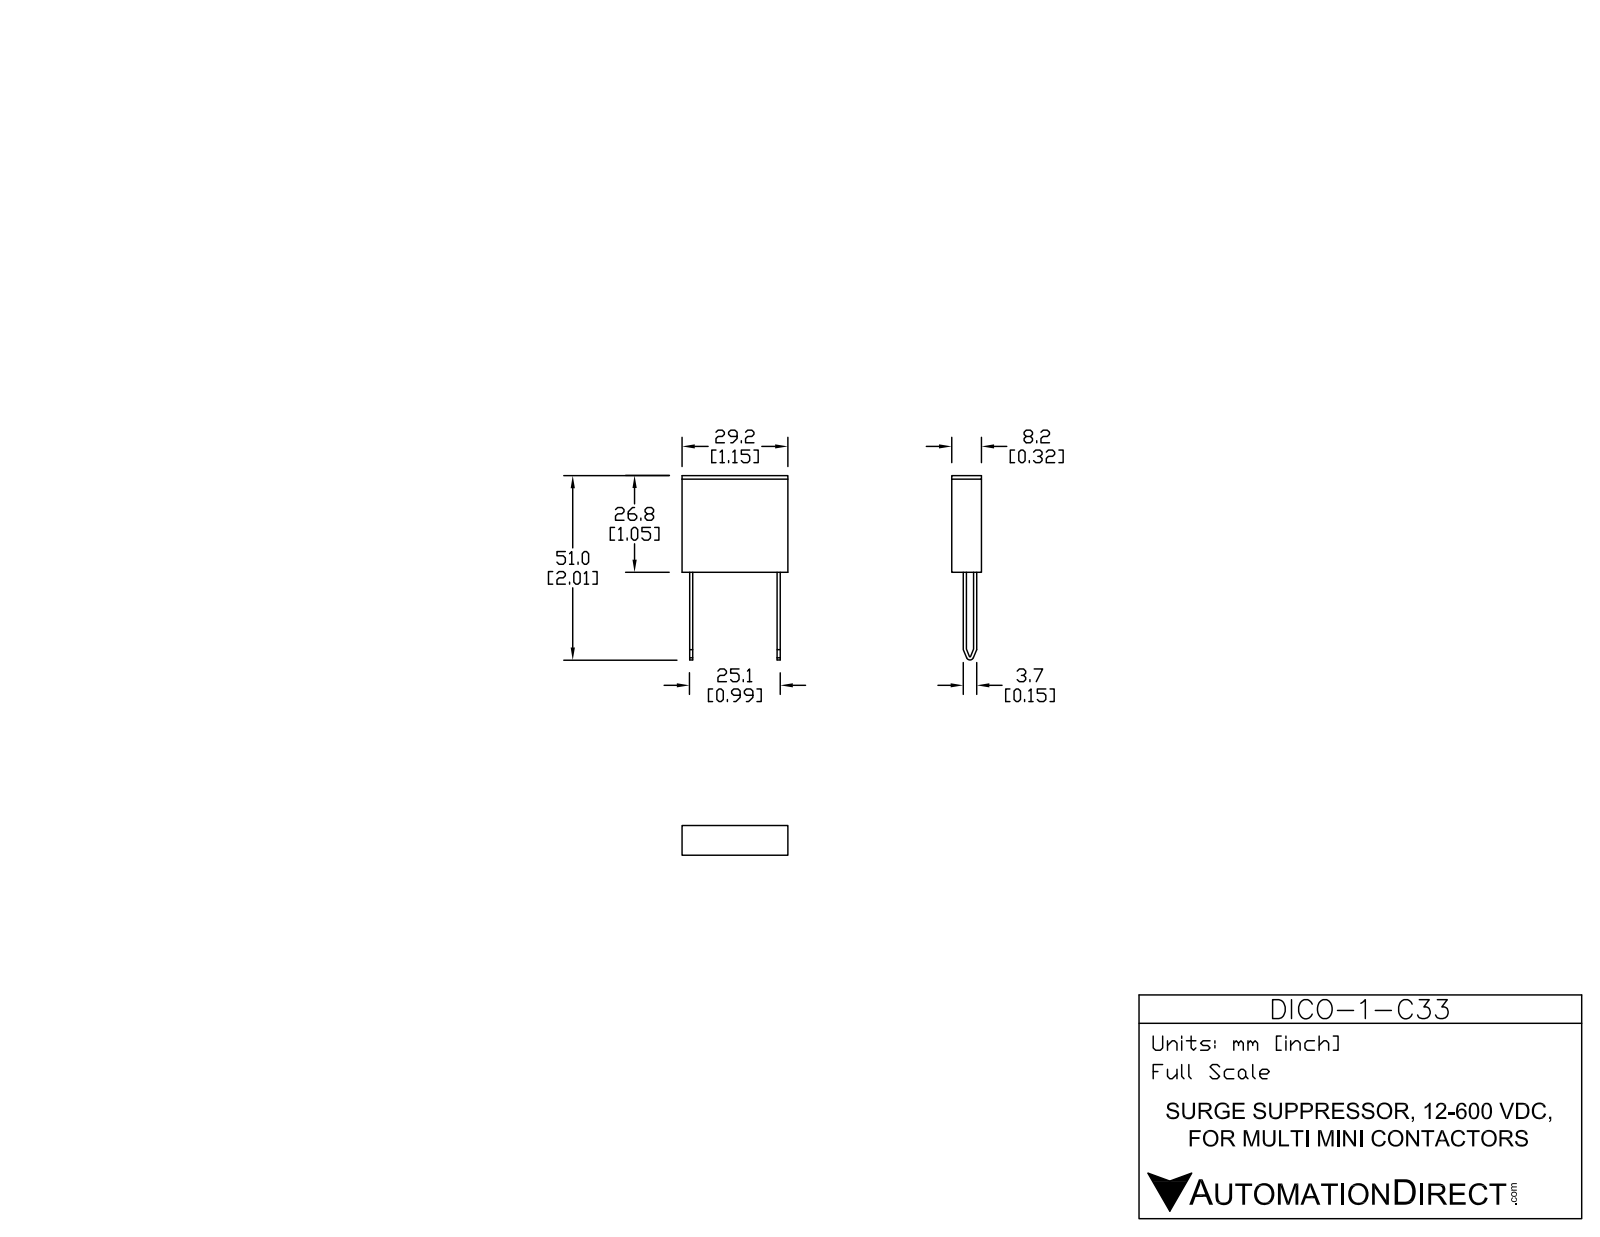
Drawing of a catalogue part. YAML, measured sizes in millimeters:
part_name: "DIC0-1-C33"
step_written_by: "SolidWorks 2013 (AUTOMOTIVE_DESIGN)"
units: millimeters
bodies: {solids: 1, faces: 34, planar: 26, cylindrical: 8, other: 0}
overall_size: [50.9, 29.2, 8.2]
volume: 6463
surface_area: 2803
partial_cylinders:
  - {radius: 0.15, count: 1}
  - {radius: 1, count: 1}
face_to_face_distances: [8.2, 26.7, 29.2, 0.85, 2.1, 27.1, 2.95, 26.25, 24.15, 2.85]
